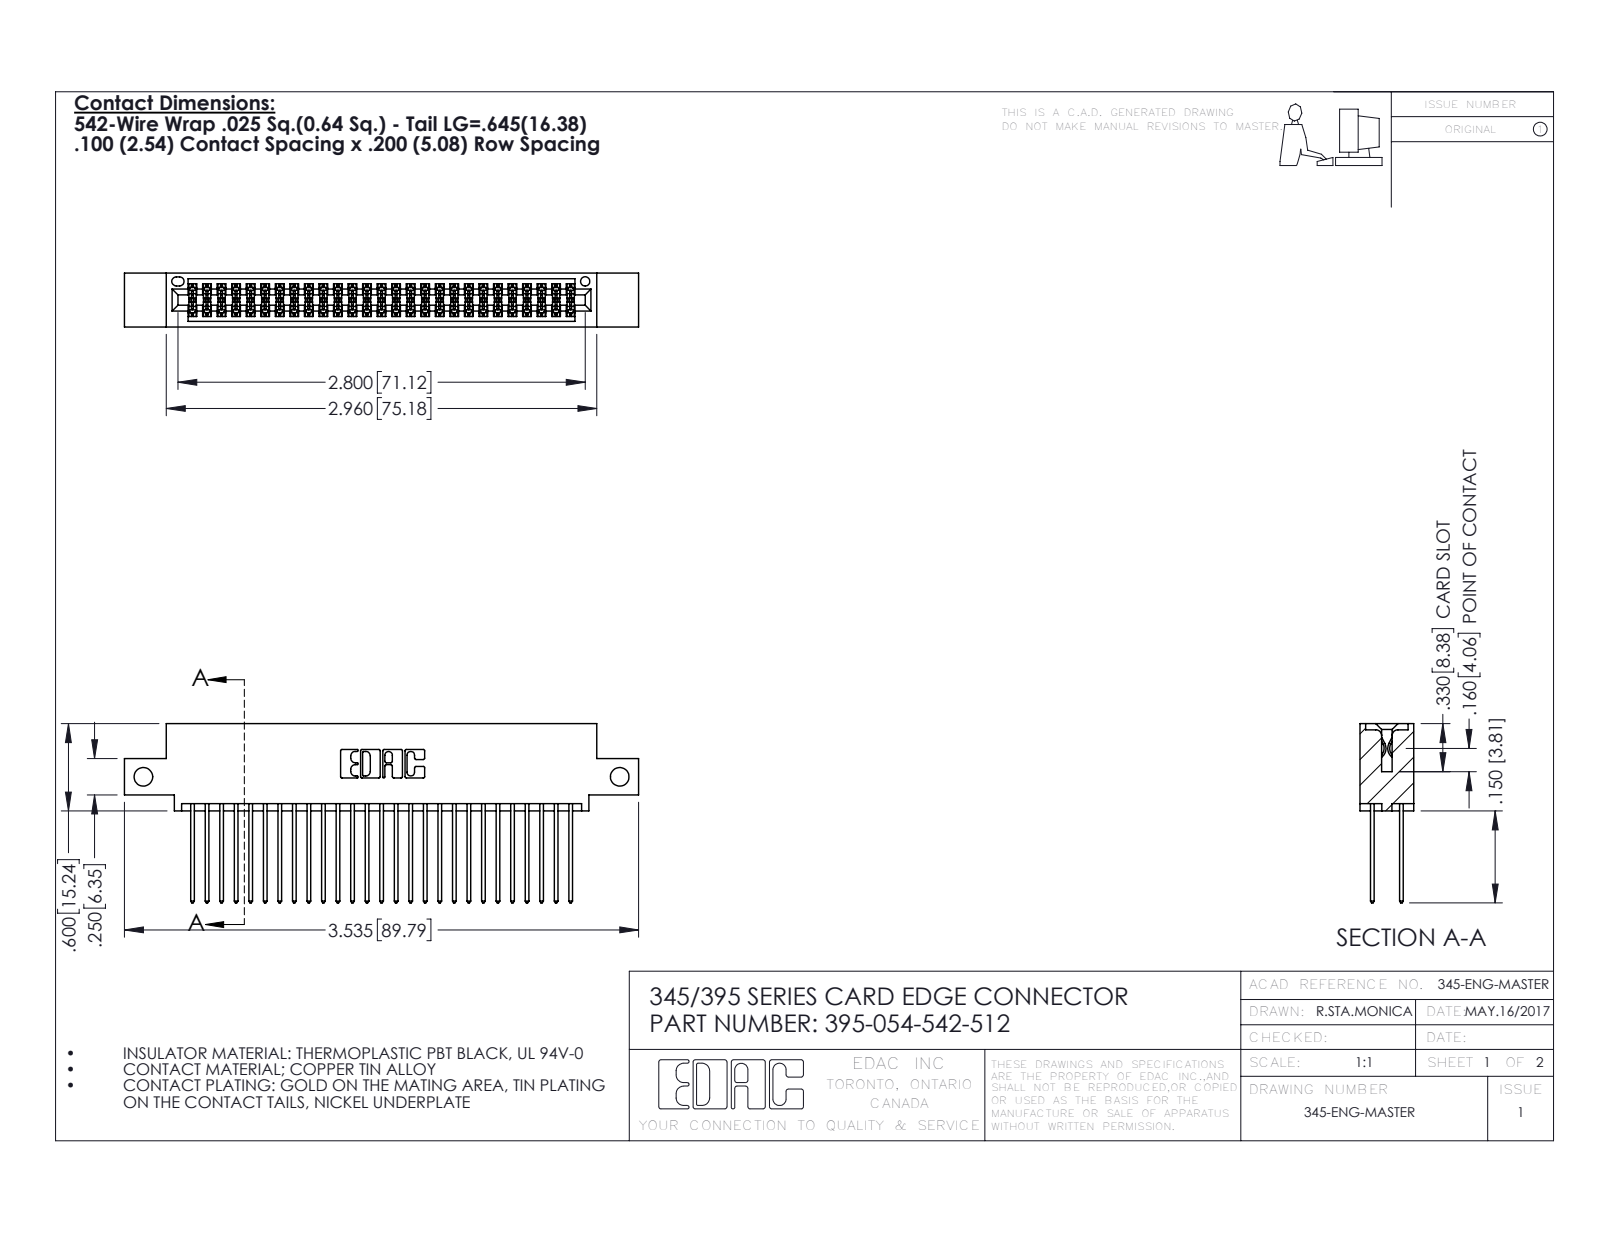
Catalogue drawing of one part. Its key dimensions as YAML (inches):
part_name: "395-054-542-512; 345-292-001_345-293-142; 345 Part_0.110 Offset - Side Mount"
step_written_by: "SolidWorks 2016 (CONFIG_CONTROL_DESIGN)"
units: inches
bodies: {solids: 55, faces: 2830, planar: 1866, cylindrical: 964, other: 0}
overall_size: [3.535, 1.232, 0.37]
volume: 0.529
surface_area: 21.18
round_holes:
  - {diameter: 0.128, count: 2}
  - {diameter: 0.064, count: 1}
partial_cylinders:
  - {radius: 0.006, count: 81}
  - {radius: 0.01, count: 54}
  - {radius: 0.01, count: 22}
  - {radius: 0.007, count: 6}
  - {radius: 0.031, count: 6}
  - {radius: 0.026, count: 3}
  - {radius: 0.014, count: 2}
  - {radius: 0.019, count: 2}
face_to_face_distances: [0.298, 0.072, 0.2, 0.098, 0.272, 0.025, 0.37, 0.225, 0.175, 0.149]
hole_center_spacings: [3.275]
